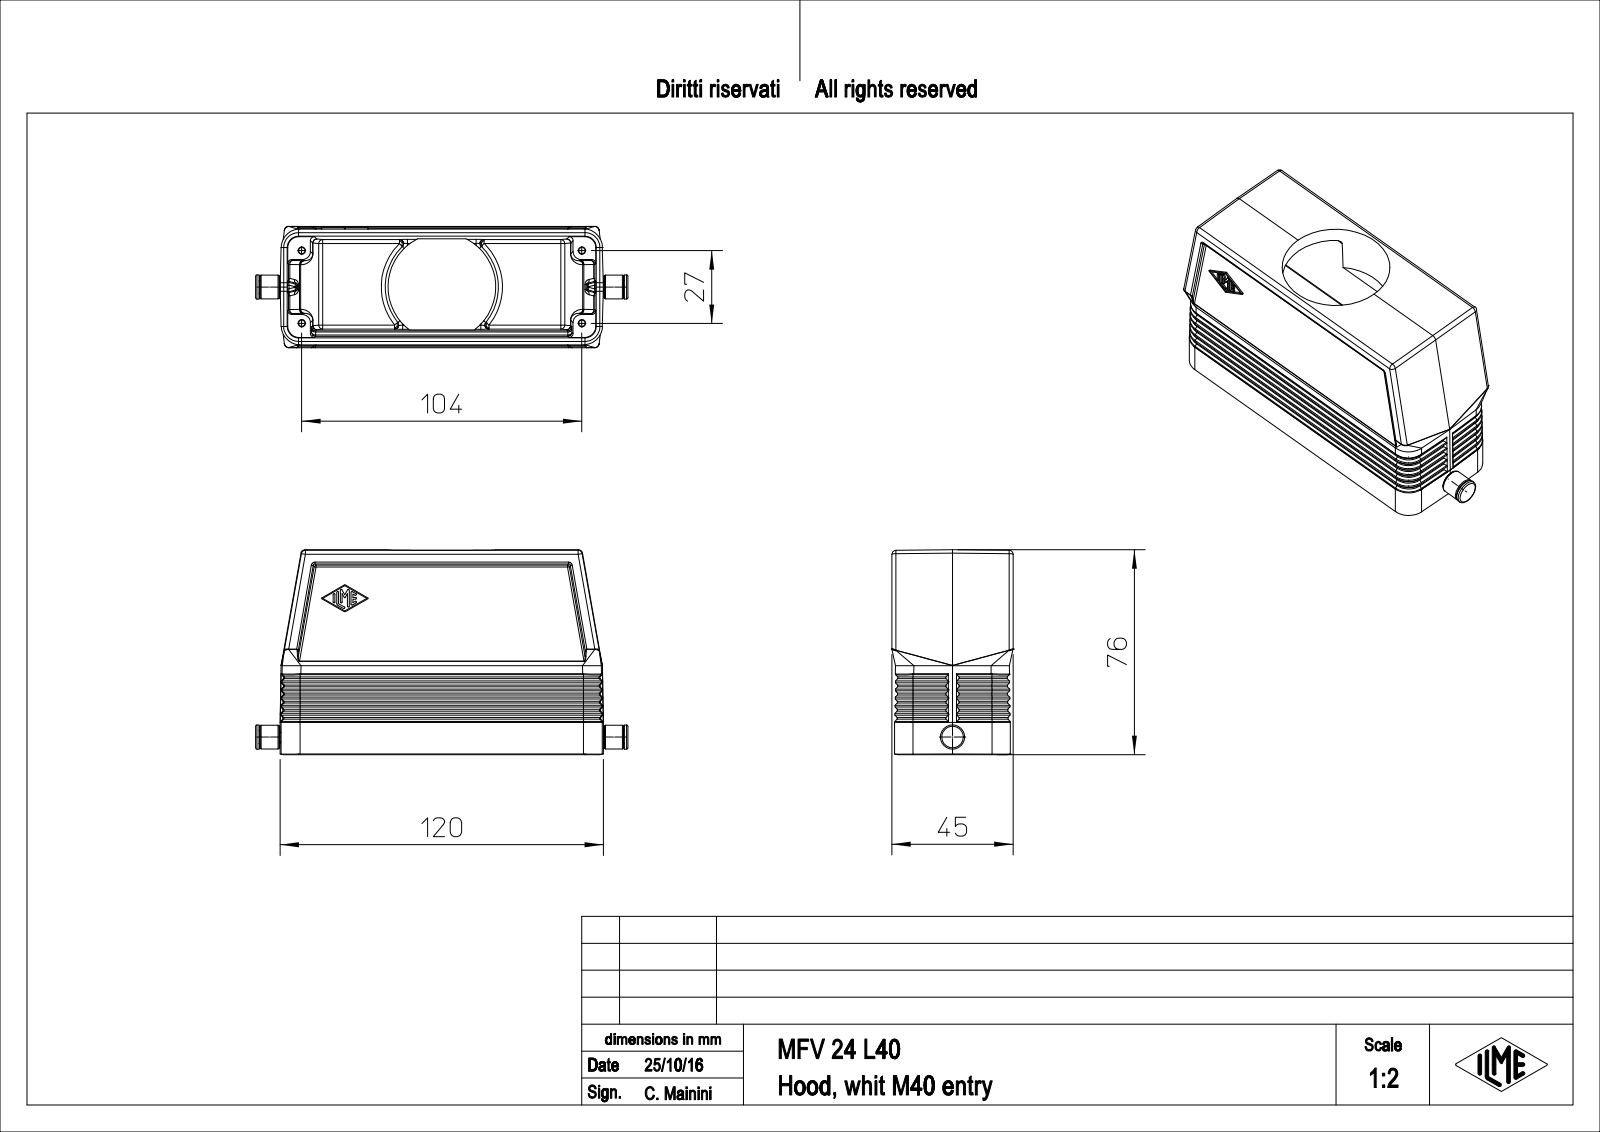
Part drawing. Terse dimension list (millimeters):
name: MFV_24_L40
written by: PTC Creo Elements/Direct Modeling 19.0E 27-Jun-2016 (C) Parametric Technology GmbH (AUTOMOTIVE_DESIGN)
unit: mm
bodies: 1 solid, 529 faces (220 planar, 149 cylindrical, 160 other)
size: 138.2 × 76 × 45
volume: 102 848 mm³; area: 53 838 mm²
holes: 4× ⌀2.75, 1× ⌀40
bosses: 1× ⌀9, 1× ⌀8.8, 1× ⌀4.8, 1× ⌀3.2
rounds: 78× R0.5, 11× R1.5, 8× R7, 4× R3, 4× R4.2, 1× R21
face distances: 43, 2.01, 2, 4, 44, 1, 8.45, 6, 6.01, 4.01
hole spacings: 53.72, 27, 104, 107.45
